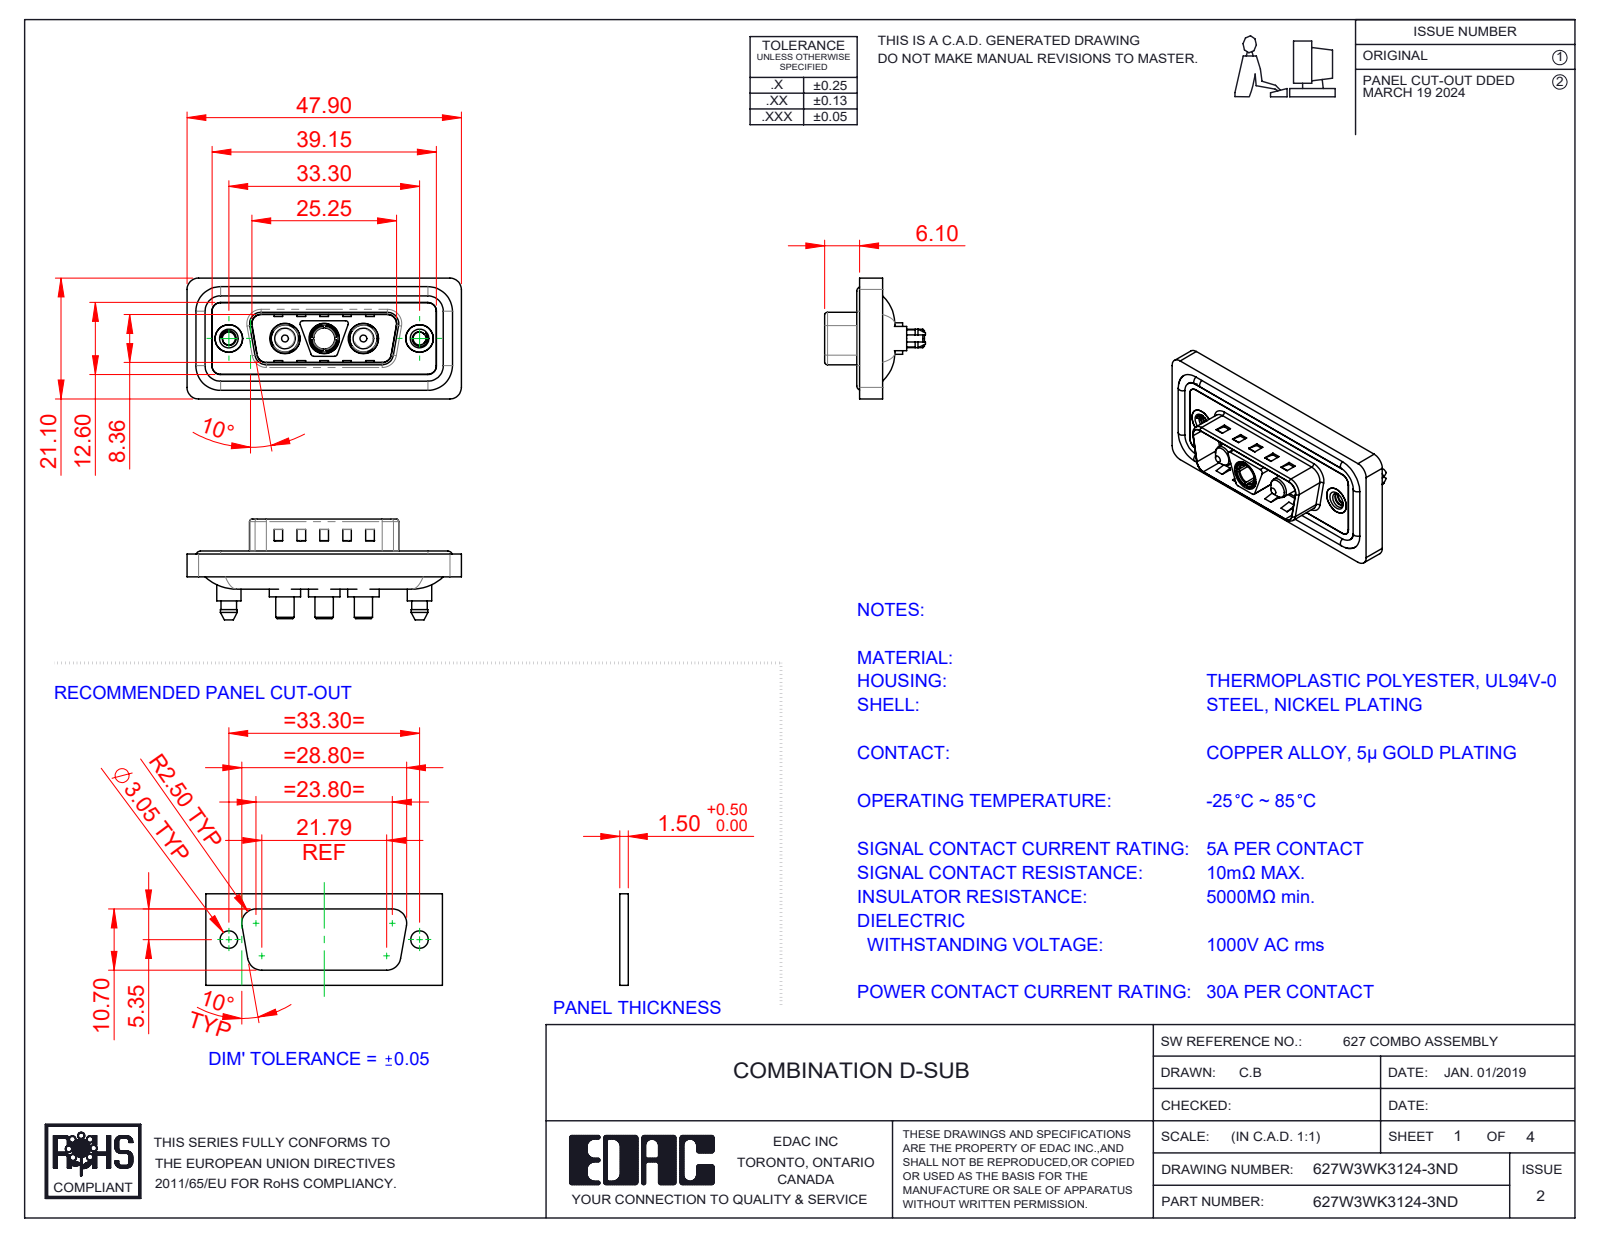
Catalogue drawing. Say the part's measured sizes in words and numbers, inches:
The part is named "627Combo Waterproof Housing_15 Contacts; 627Combo Housing_3WK3; 627Combo Shell Rear_15 Contacts; Power Pin_30A S (+5 more)". Its 3-D file was written by "SolidWorks 2023 (CONFIG_CONTROL_DESIGN)". It is 13 solids with 667 faces: 247 planar, 290 cylindrical and 130 other. Overall it measures 1.886 by 0.831 by 0.693 inches. Its volume is 0.357 cubic inches and its surface area 14.69 square inches. Round holes: 3 of diameter 0.191, 3 of diameter 0.209, 2 of diameter 0.089, 2 of diameter 0.157, 2 of diameter 0.189, 2 of diameter 0.197, 1 of diameter 0.146. Round bosses or shafts: 4 of diameter 0.063, 3 of diameter 0.217, 3 of diameter 0.205, 3 of diameter 0.187, 3 of diameter 0.148, 3 of diameter 0.126, 2 of diameter 0.213, 2 of diameter 0.193. Partial cylindrical surfaces (rounded edges, fillets, slot ends): 28 of radius 0.059, 20 of radius 0.079, 12 of radius 0.02, 10 of radius 0.063, 4 of radius 0.01, 4 of radius 0.024, 4 of radius 0.026, 4 of radius 0.035. The main face-to-face distances are 0.016, 0.043, 0.059, 0.02, 0.122, 0.063, 0.114, 0.157, 0.028, 0.032. The hole center spacings are 0.27, 0.386, 0.656, 0.925, 0.539, 1.311.
